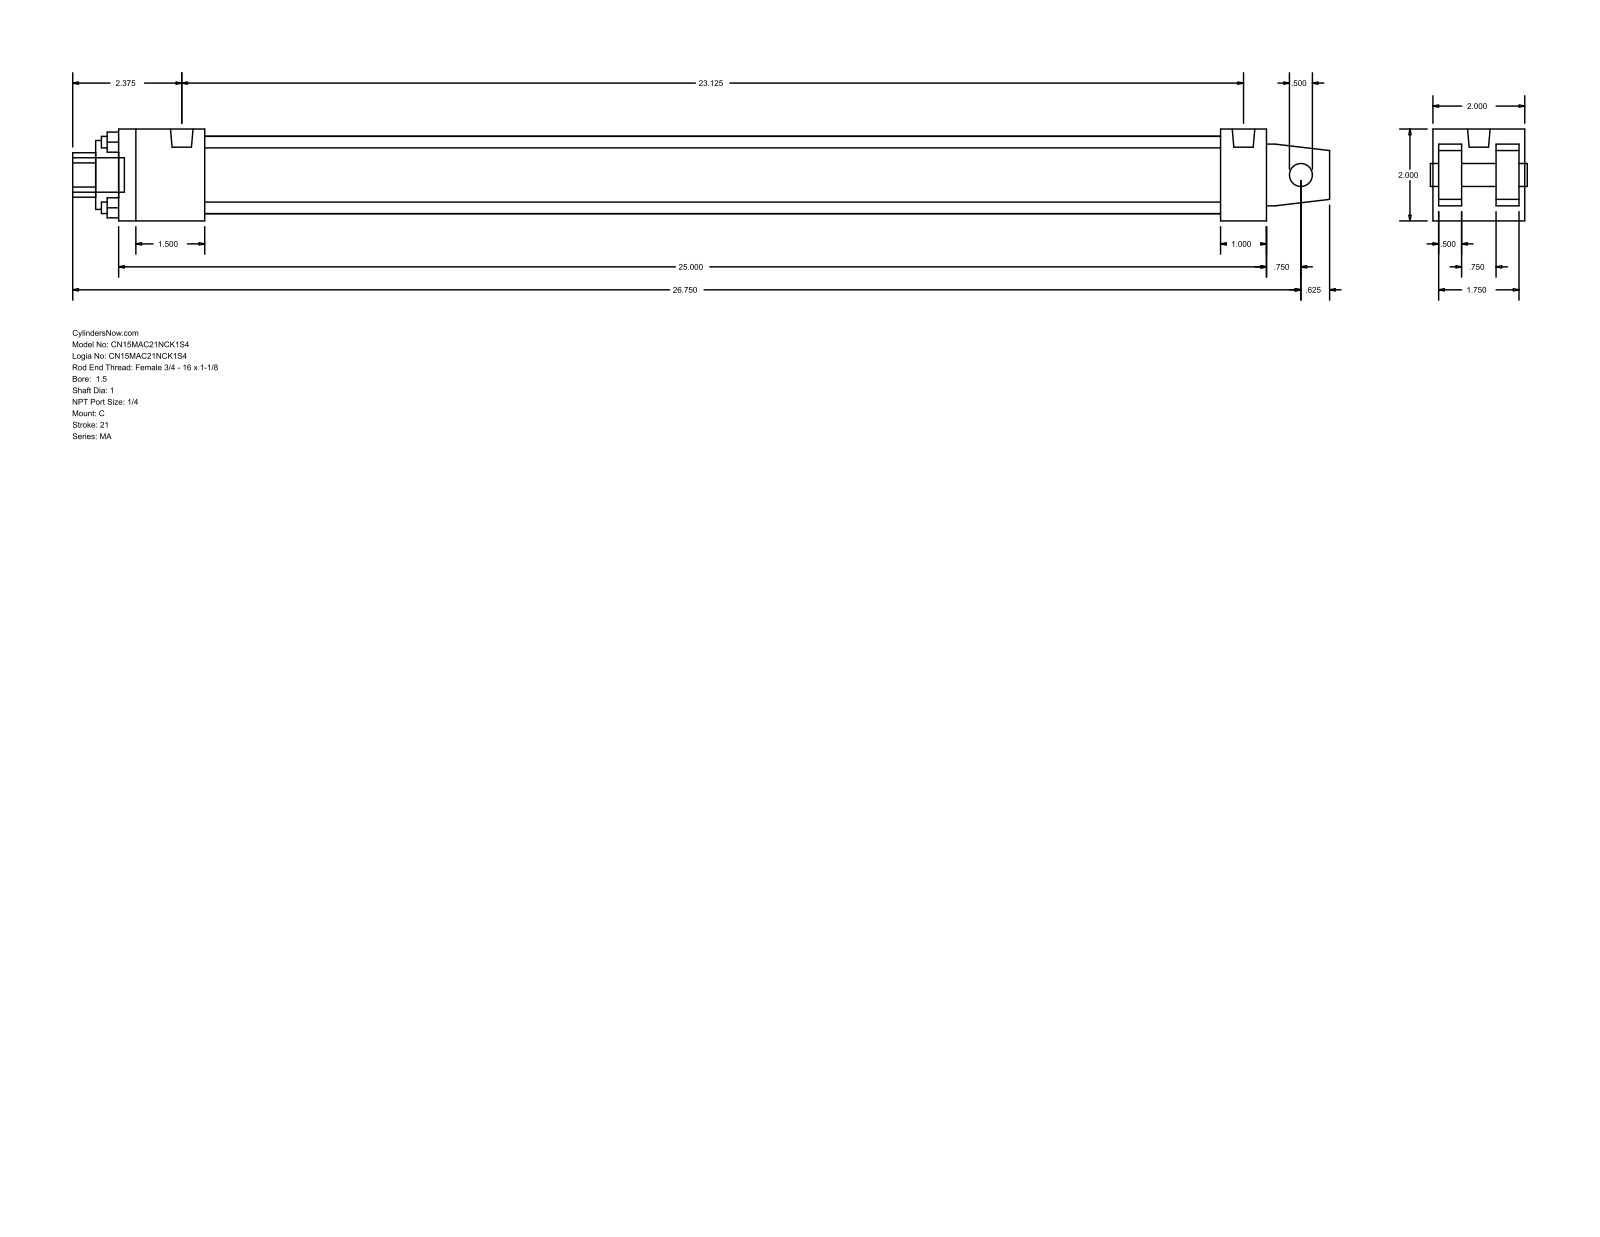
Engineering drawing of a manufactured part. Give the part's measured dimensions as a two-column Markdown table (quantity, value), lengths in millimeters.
| quantity | value |
| --- | --- |
| part name | MA_C__0150_1 |
| STEP written by | GSSL Pune (CONFIG_CONTROL_DESIGN) |
| units | millimeters |
| bodies | 0 solids, 103 faces (76 planar, 27 cylindrical, 0 other) |
| overall size | 695.33 × 50.8 × 50.8 |
| round holes (diameter × count) | 6.35 × 4, 12.7 × 1, 25.4 × 1, 38.1 × 1, 42.93 × 1 |
| round bosses / shafts (diameter × count) | 7.94 × 4, 12.49 × 2, 19.05 × 1 |
| partial cylindrical surfaces (radius × count) | 12.29 × 1 |
| main face-to-face distances | 50.8, 47.63, 12.7, 34.93, 3.17, 15.87, 31.76, 60.33, 622.3, 44.46 |
| hole center spacings | 25.68, 36.32, 51.36 |
